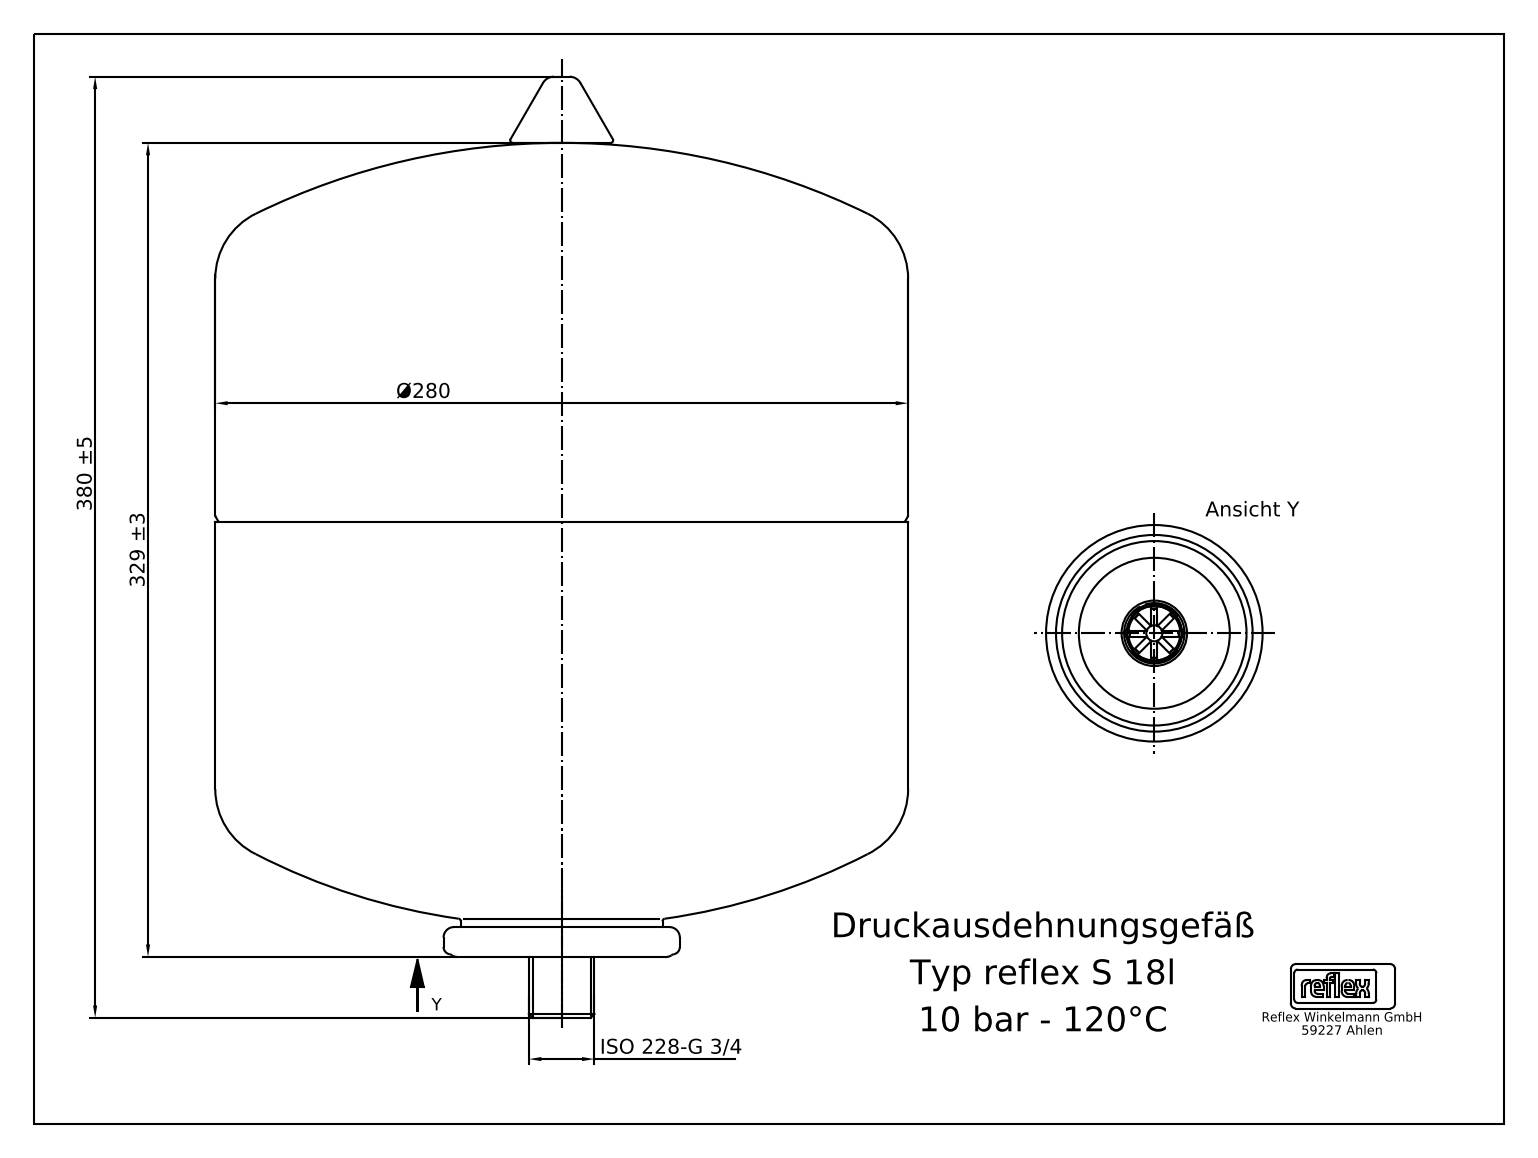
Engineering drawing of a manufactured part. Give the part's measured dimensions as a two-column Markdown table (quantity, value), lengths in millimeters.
| quantity | value |
| --- | --- |
| STEP written by | Mechanical Desktop 2008 (CONFIG_CONTROL_DESIGN) |
| units | millimeters |
| bodies | 13 solids, 151 faces (71 planar, 46 cylindrical, 34 other) |
| overall size | 380 × 280.32 × 280 |
| volume | 17 200 000 mm³ |
| surface area | 618 576 mm² |
| round holes (diameter × count) | 14.1 × 1, 18.9 × 1 |
| round bosses / shafts (diameter × count) | 280 × 1, 96 × 1, 82 × 1, 26.9 × 1, 17.1 × 1, 9 × 1, 6 × 1 |
| partial cylindrical surfaces (radius × count) | 1.12 × 4, 0.45 × 3, 0.77 × 2, 1.35 × 2, 1.85 × 2, 1.88 × 2, 2.54 × 2, 0.56 × 1 |
| main face-to-face distances | 206, 49, 255, 13, 62, 268, 164.5, 151.5, 102.5, 103.5 |
